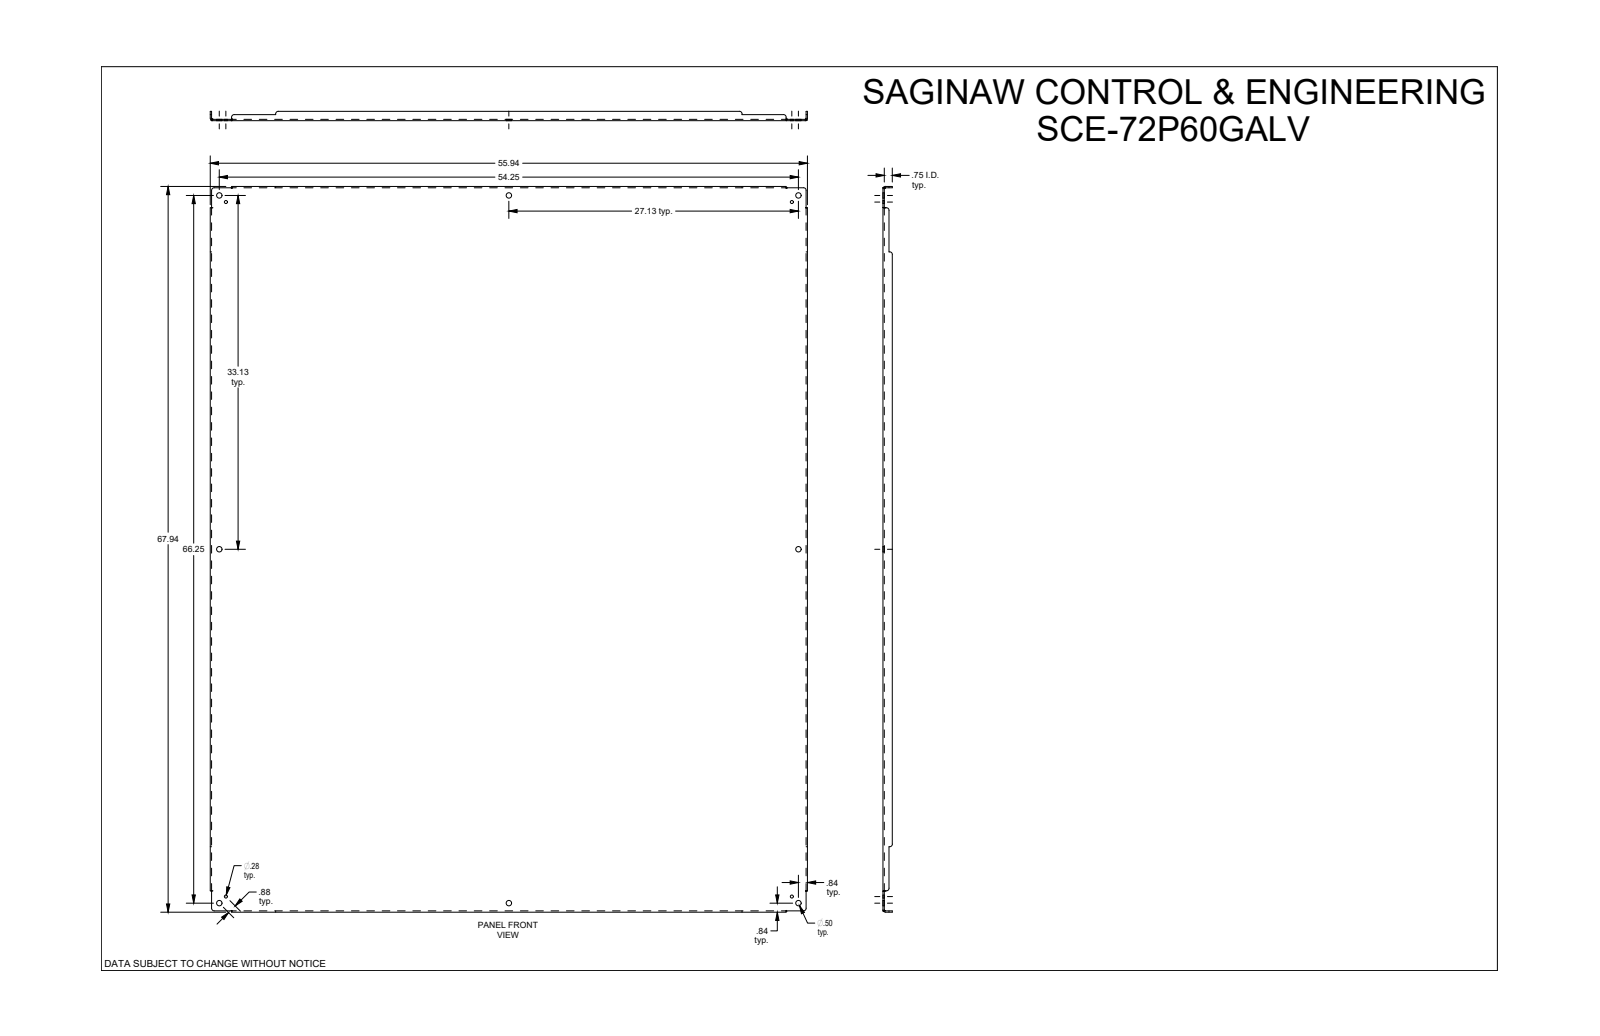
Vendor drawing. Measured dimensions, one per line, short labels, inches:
name: SCE-72P60GALV
written by: SolidWorks 2019 (CONFIG_CONTROL_DESIGN)
unit: in
bodies: 1 solid, 110 faces (46 planar, 40 cylindrical, 24 other)
size: 67.938 × 55.938 × 0.875
volume: 492.8 in³; area: 7 918 in²
holes: 8× ⌀0.5, 4× ⌀0.281
rounds: 12× R0.25, 4× R0.112, 4× R0.237
face distances: 0.125, 0.125, 55.813, 67.813, 55.687, 55.938, 67.687, 67.938, 0.75, 0.875
hole spacings: 0.875, 26.513, 27.125, 32.512, 33.125, 42.814, 53.635, 62.713
